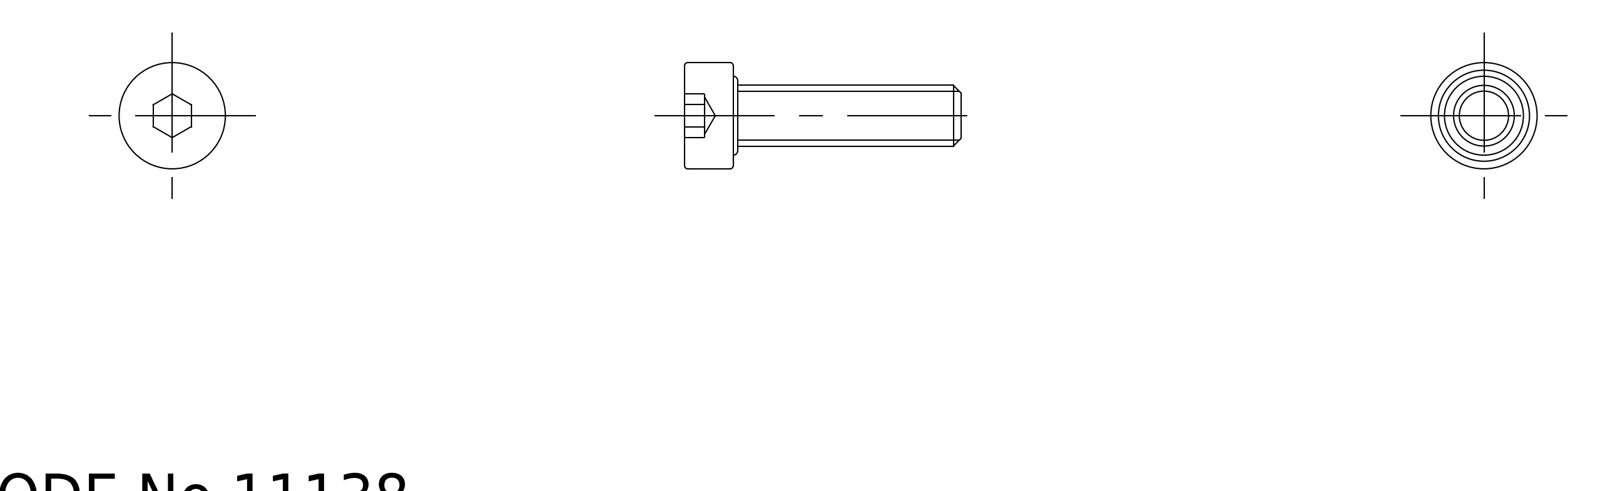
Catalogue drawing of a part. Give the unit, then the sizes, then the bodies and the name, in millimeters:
Units: millimetres
Overall size (bounding box): 18.2 × 7 × 7
Round holes (diameter × count): ⌀6 ×1
Round bosses / shafts (diameter × count): ⌀7 ×1, ⌀4 ×1
Main face-to-face distances: 2.9, 18.2, 15.3, 3.2, 15, 2.5, 1.3, 1.6, 1.9, 16.9
Volume: 302 mm³ · Surface area: 376 mm²
Bodies: 2 solids, 27 faces (11 planar, 6 cylindrical, 10 other)
Part name (STEP PRODUCT): screw; TL_418_M4_15
STEP written by: SolidWorks 2015 (AUTOMOTIVE_DESIGN)
